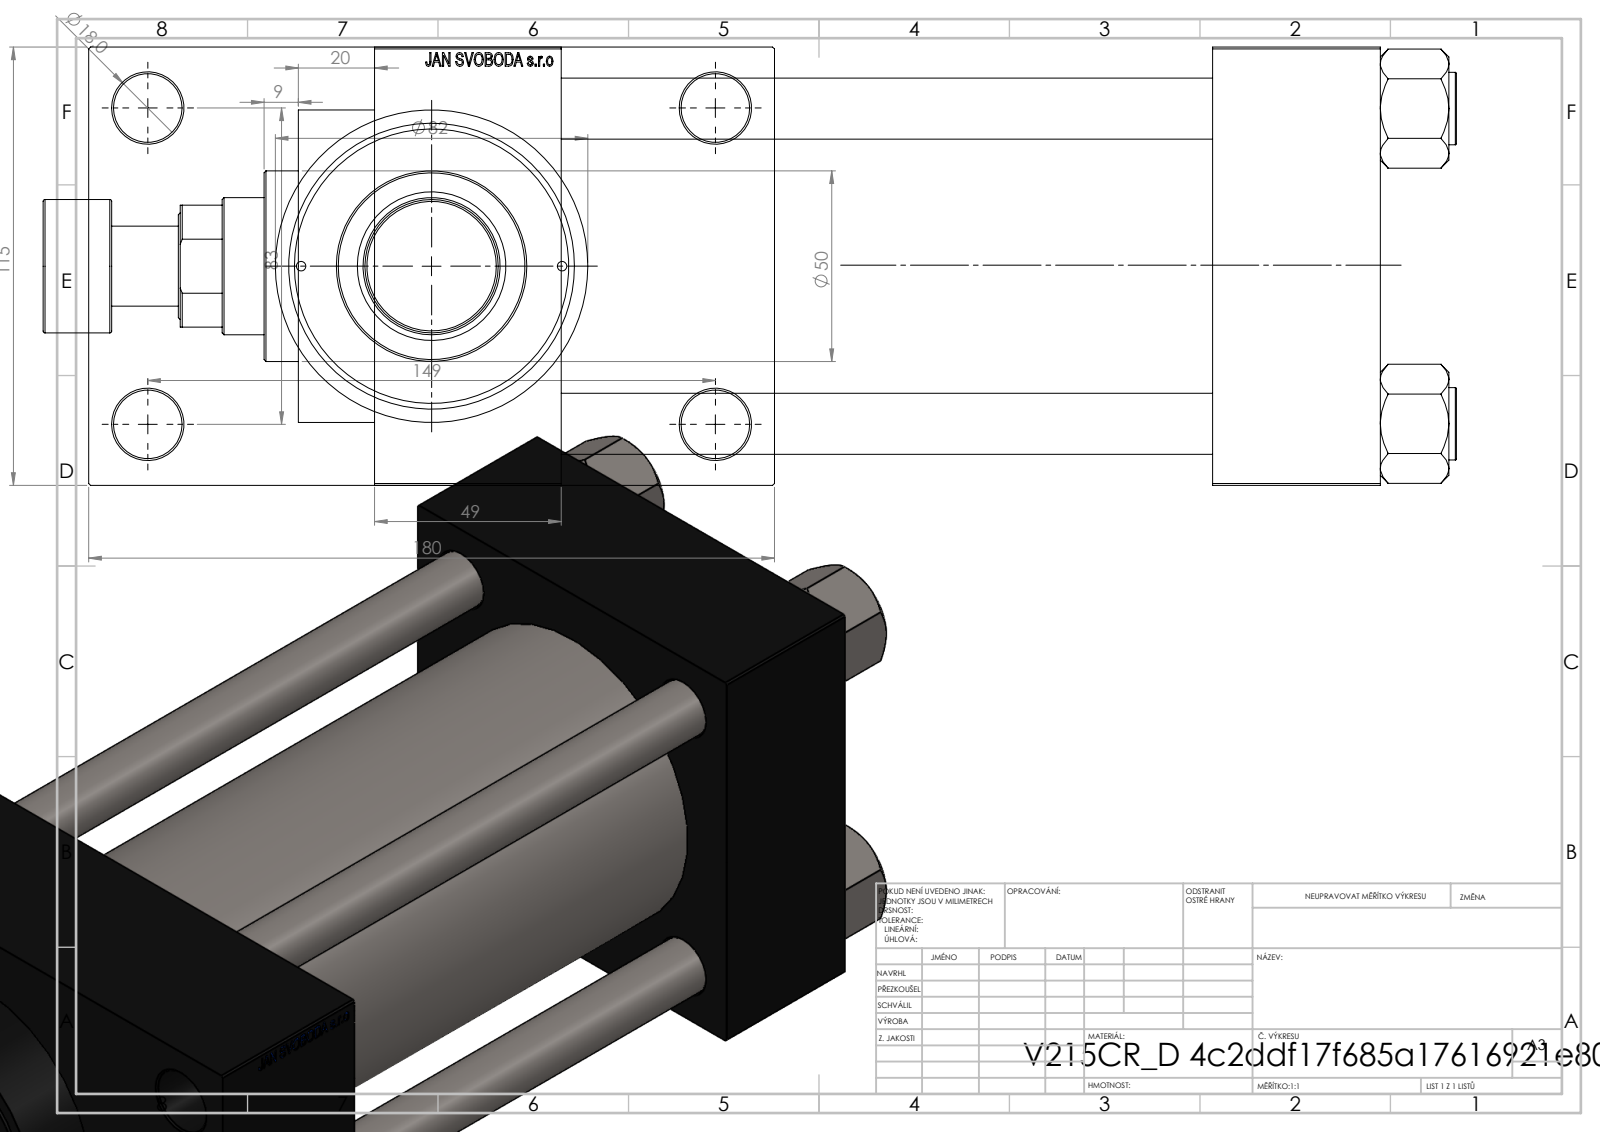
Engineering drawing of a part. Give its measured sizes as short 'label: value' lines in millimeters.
name: V215CR_ROD_END_F; V215CR_D_TYCINKA; V215CR_VCP_D; V215_VC_A (+2 more)
written by: SolidWorks 2019 (CONFIG_CONTROL_DESIGN)
unit: mm
bodies: 12 solids, 1174 faces (551 planar, 97 cylindrical, 526 other)
size: 371 × 180 × 115
volume: 2 294 000 mm³; area: 387 092 mm²
holes: 4× ⌀16, 4× ⌀18, 2× ⌀2.5, 2× ⌀7, 2× ⌀26.44, 2× ⌀35, 1× ⌀25.5, 1× ⌀36, 1× ⌀39, 1× ⌀61, 1× ⌀72, 1× ⌀80
bosses: 4× ⌀19, 1× ⌀86, 1× ⌀82, 1× ⌀50, 1× ⌀35, 1× ⌀21
face distances: 115, 171, 49, 220, 44, 215, 264, 32.5, 147.5, 180
hole spacings: 33.15, 41.96, 57.81, 58.48, 82.7, 85.28, 86.17, 89.24
